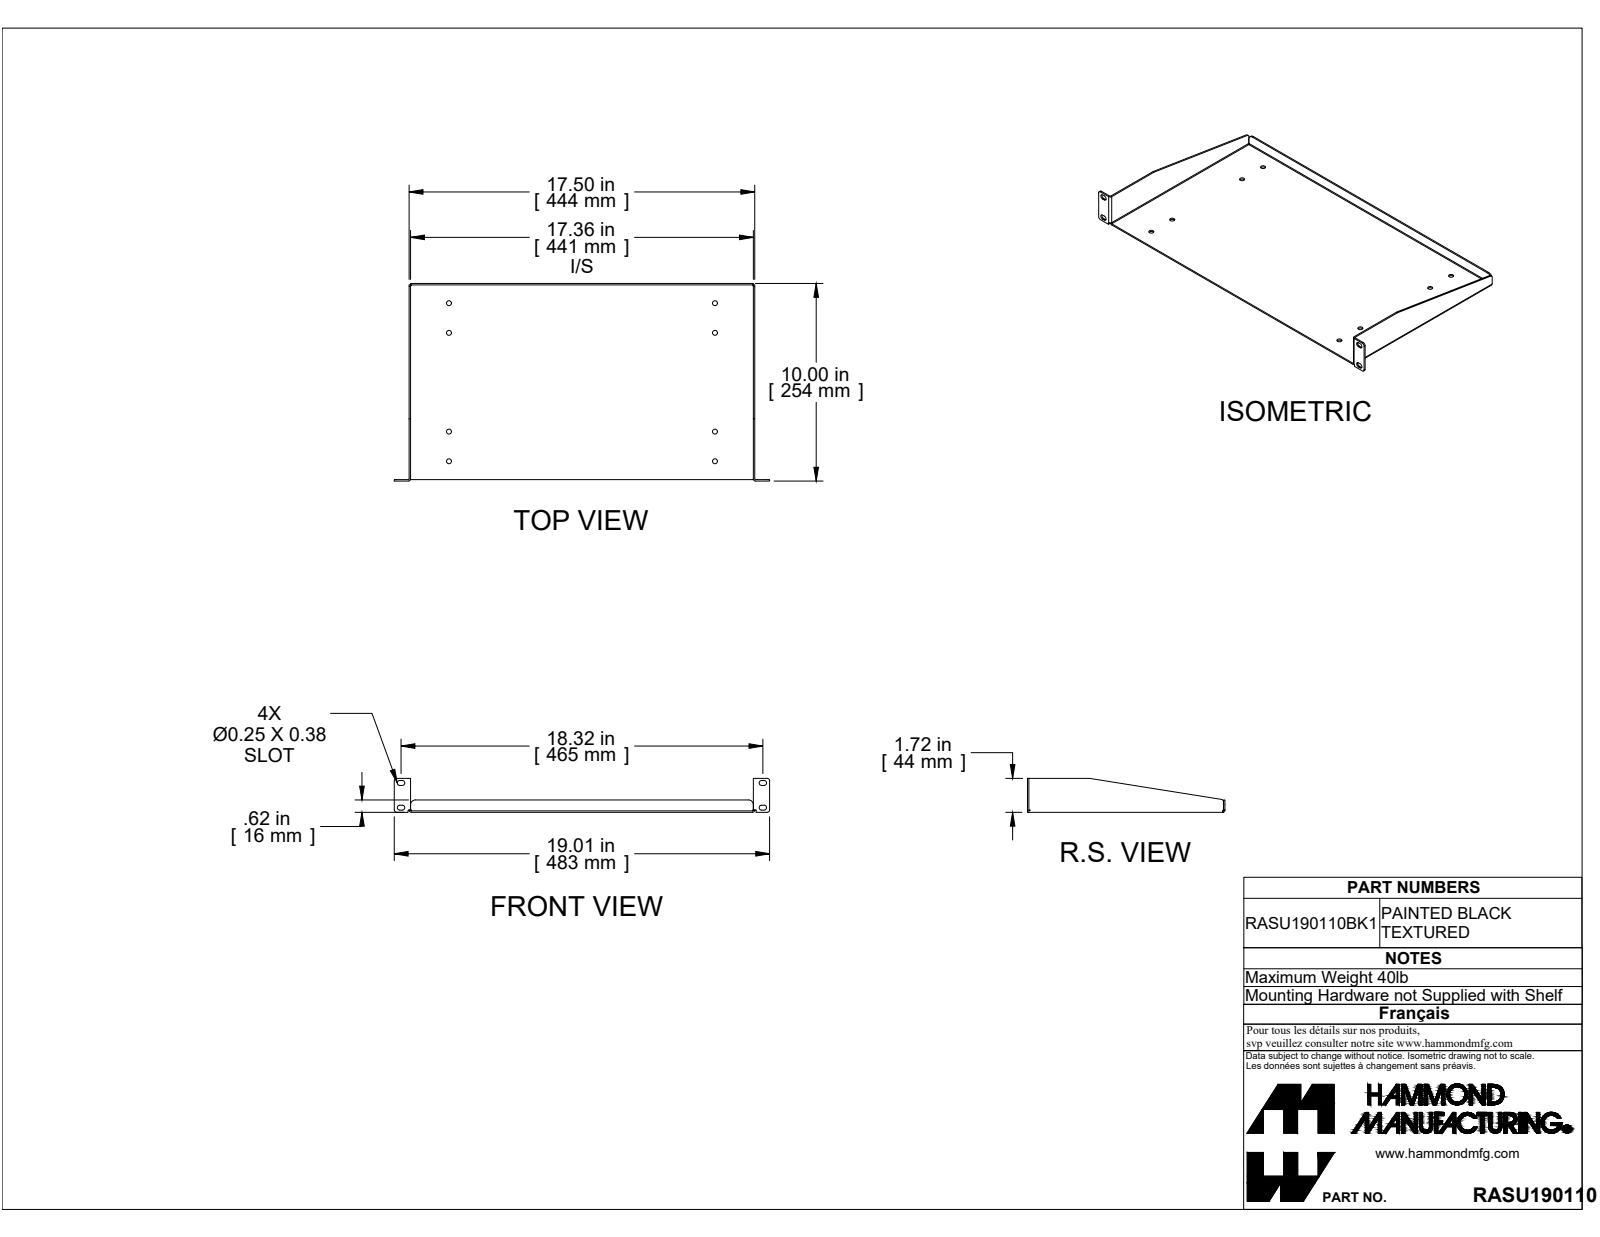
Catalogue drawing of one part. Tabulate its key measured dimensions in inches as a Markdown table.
| quantity | value |
| --- | --- |
| part name | RASU190110BK1 |
| STEP written by | SolidWorks 2019 (CONFIG_CONTROL_DESIGN) |
| units | inches |
| bodies | 1 solid, 88 faces (48 planar, 36 cylindrical, 4 other) |
| overall size | 19.006 × 10 × 1.718 |
| volume | 15.06 in³ |
| surface area | 423.8 in² |
| round holes (diameter × count) | 0.25 × 8 |
| partial cylindrical surfaces (radius × count) | 0.125 × 12, 0.036 × 5, 0.108 × 5, 0.055 × 3, 0.25 × 2 |
| main face-to-face distances | 0.072, 17.428, 17.356, 17.5, 9.856, 9.928, 0.072, 9.928, 10, 0.625 |
| hole center spacings | 1.5, 6.5, 13.468, 13.551, 14.954, 5, 8, 14.366 |
